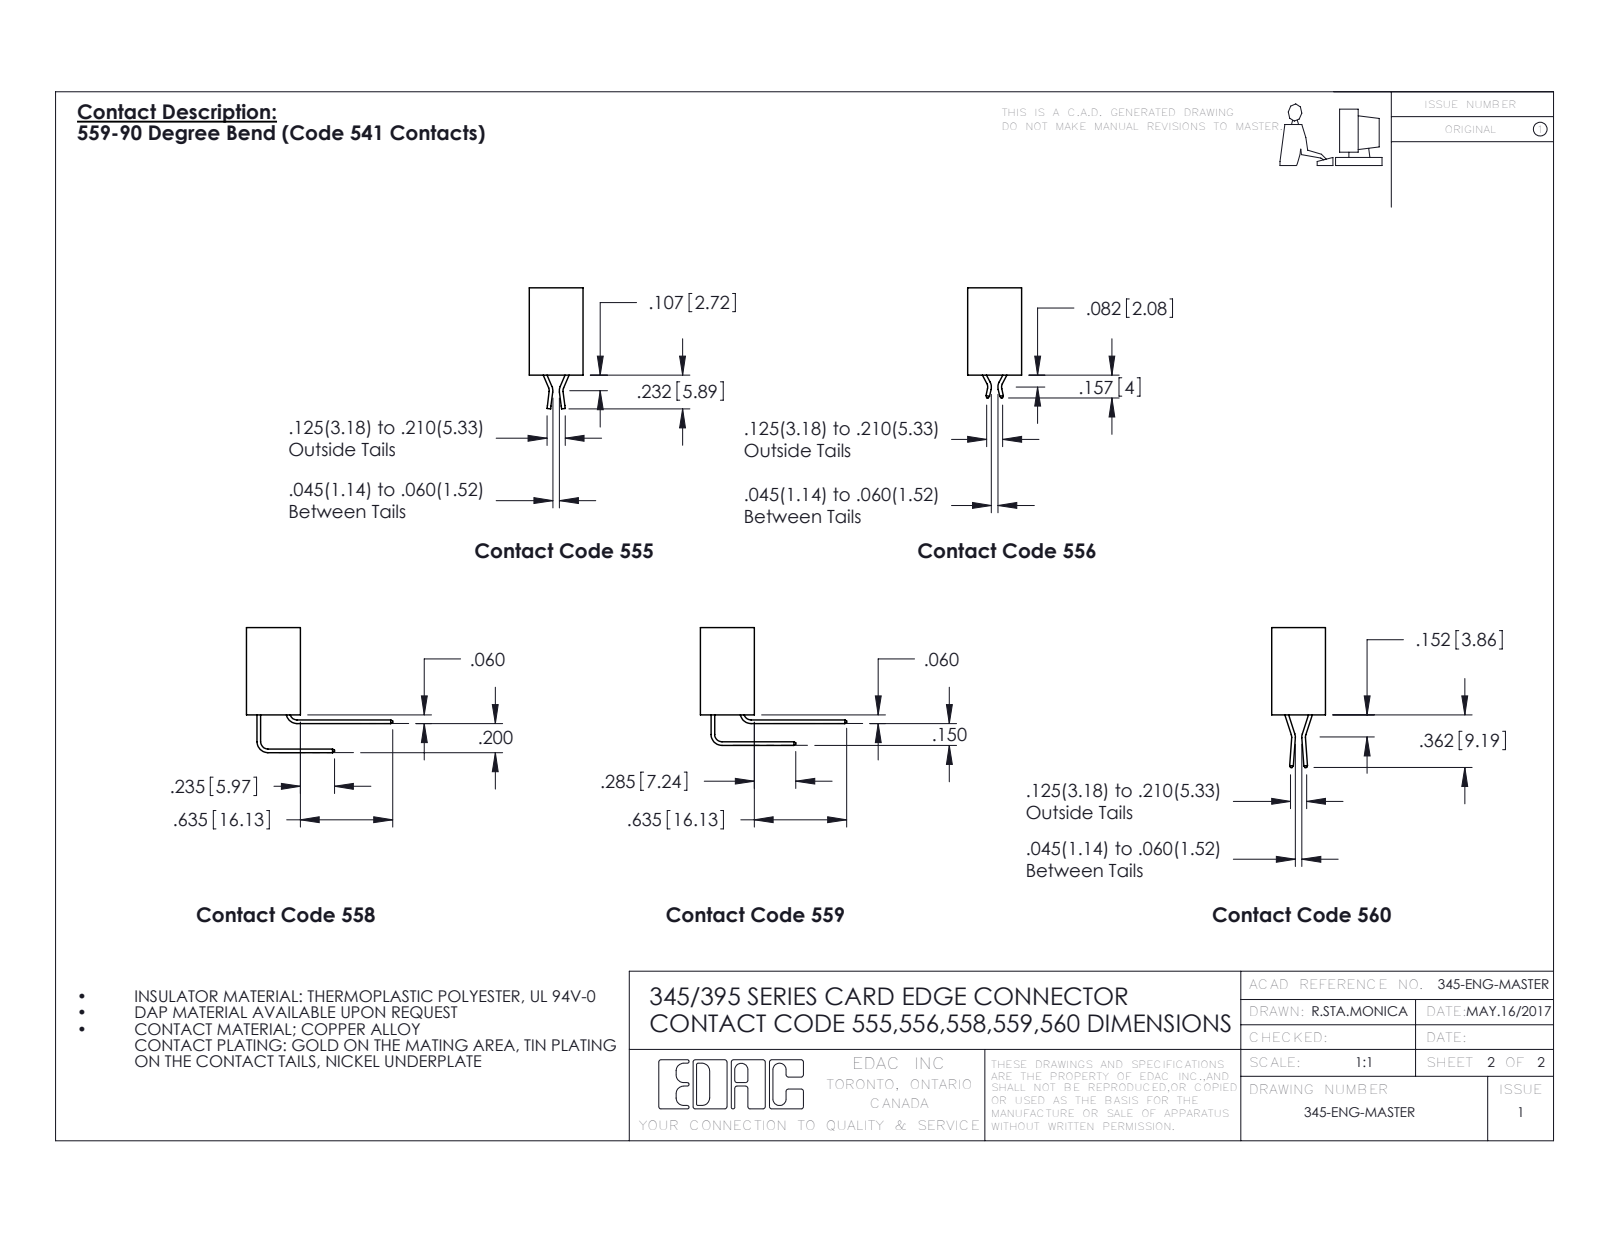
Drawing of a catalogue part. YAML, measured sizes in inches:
part_name: "345-292-001_558 559 Tail - 1; 345-292-001_559 Tail - 2; 345 Part_No Mounting Lugs; 395-032-559-201"
step_written_by: "SolidWorks 2016 (CONFIG_CONTROL_DESIGN)"
units: inches
bodies: {solids: 33, faces: 1782, planar: 1196, cylindrical: 586, other: 0}
overall_size: [1.86, 1.005, 0.809]
volume: 0.314
surface_area: 12.83
round_holes:
  - {diameter: 0.064, count: 1}
partial_cylinders:
  - {radius: 0.006, count: 49}
  - {radius: 0.01, count: 22}
  - {radius: 0.007, count: 6}
  - {radius: 0.031, count: 6}
  - {radius: 0.026, count: 3}
  - {radius: 0.014, count: 2}
  - {radius: 0.019, count: 2}
  - {radius: 0.022, count: 2}
face_to_face_distances: [0.072, 0.298, 0.2, 0.37, 0.098, 0.272, 0.025, 0.225, 0.15, 0.175]
